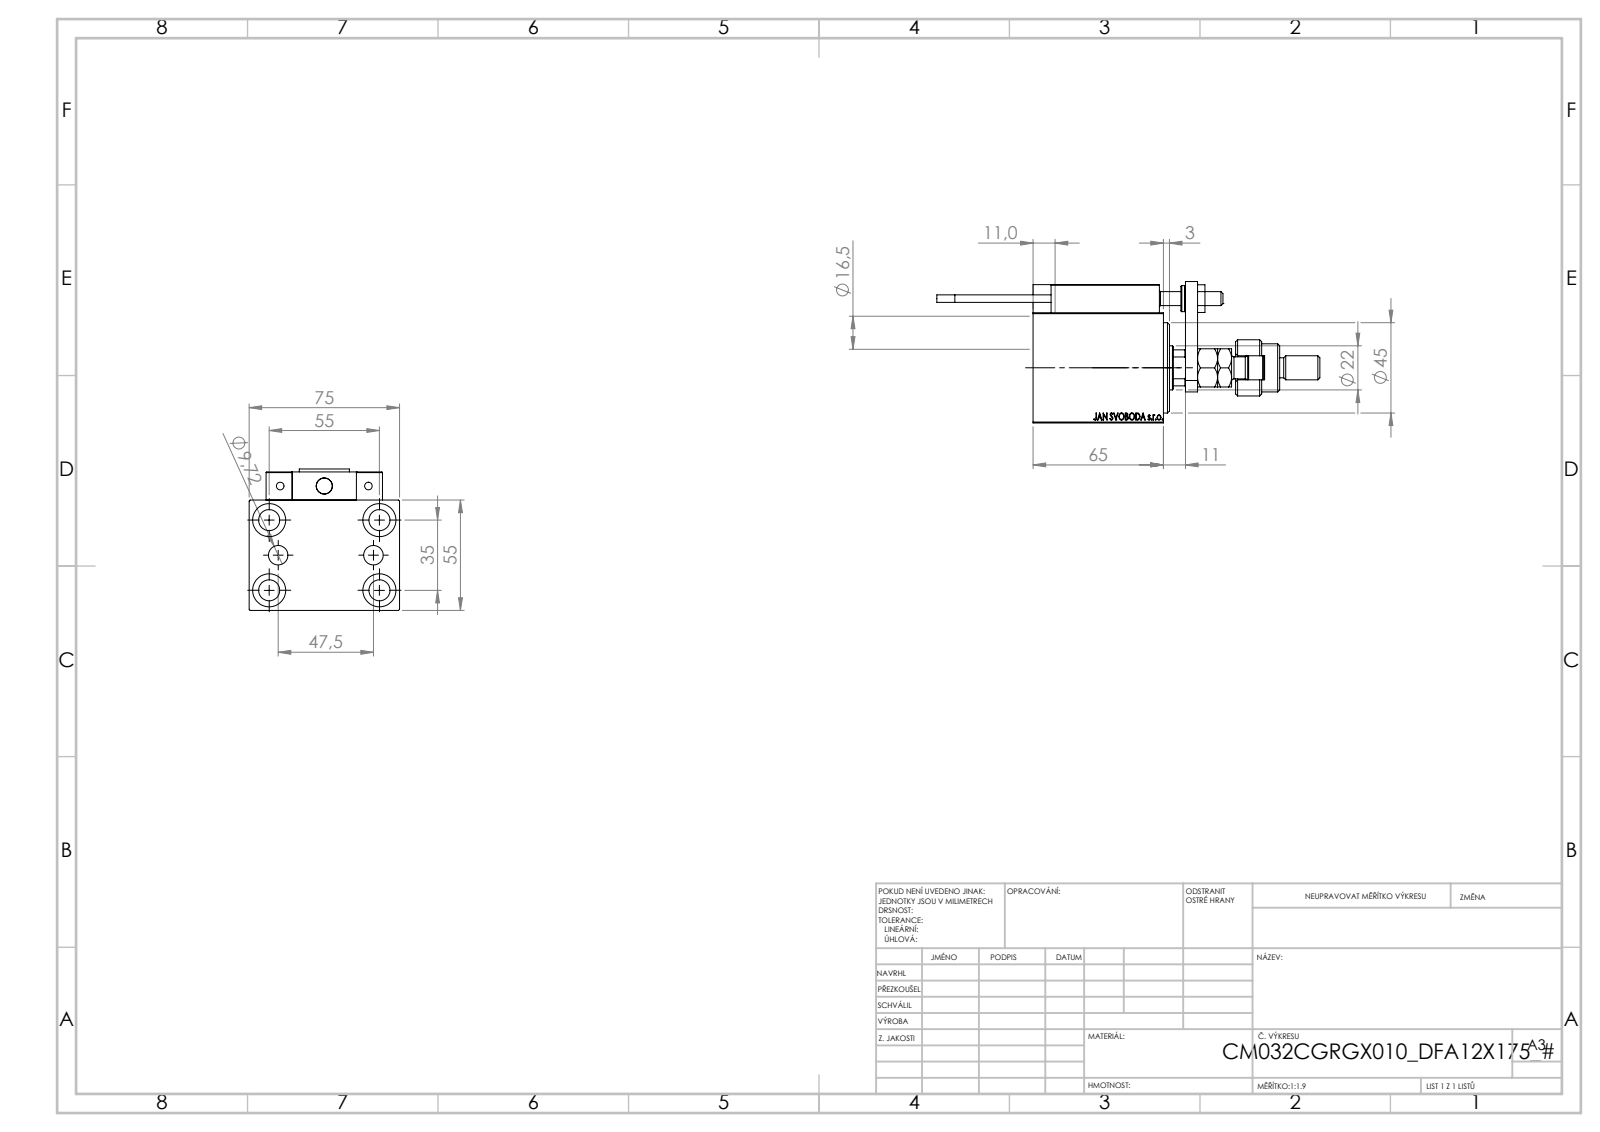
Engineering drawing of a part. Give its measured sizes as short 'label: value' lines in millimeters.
name: FEMALE_PART_FOR_DFA; MAGNET; KONCOVKA; MFA (+7 more)
written by: SolidWorks 2019 (CONFIG_CONTROL_DESIGN)
unit: mm
bodies: 25 solids, 1363 faces (588 planar, 197 cylindrical, 578 other)
size: 192 × 75 × 70.5
volume: 298 091 mm³; area: 81 807 mm²
holes: 6× ⌀4, 5× ⌀8, 5× ⌀10.5, 5× ⌀16.5, 4× ⌀3.2, 2× ⌀5, 2× ⌀9.72, 1× ⌀7, 1× ⌀22, 1× ⌀25.5, 1× ⌀32, 1× ⌀34
bosses: 2× ⌀11, 2× ⌀5, 2× ⌀3.8, 1× ⌀28, 1× ⌀24, 1× ⌀18, 1× ⌀13, 1× ⌀12
rounds: 30× R0.3, 2× R3, 1× R9.75, 1× R10.5
face distances: 55, 14, 75, 18, 5, 23, 45, 69, 10, 8
hole spacings: 17.9, 32.6, 54.16, 11.37, 17.12, 20, 23.75, 27.8
